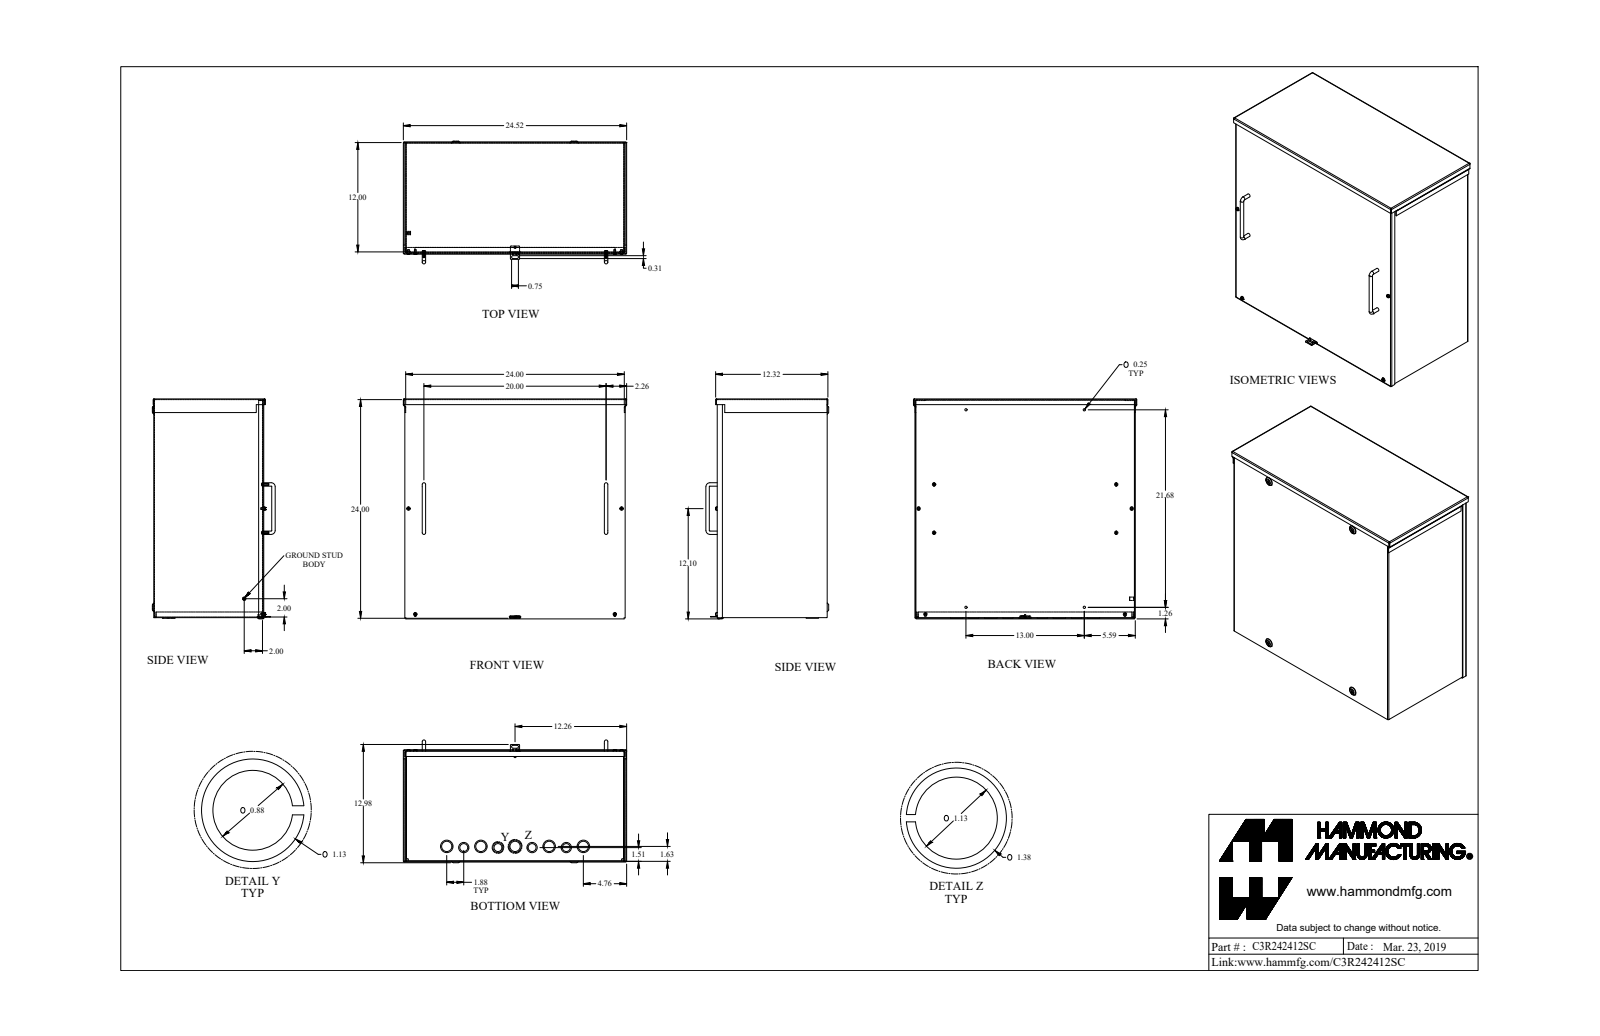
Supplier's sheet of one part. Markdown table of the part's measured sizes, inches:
| quantity | value |
| --- | --- |
| part name | C3R242412SC_Default |
| STEP written by | SolidWorks 2019 (CONFIG_CONTROL_DESIGN) |
| units | inches |
| bodies | 17 solids, 609 faces (314 planar, 177 cylindrical, 118 other) |
| overall size | 24.519 × 24.135 × 13.478 |
| volume | 179.7 in³ |
| surface area | 4 994 in² |
| round holes (diameter × count) | 0.156 × 5, 0.17 × 4, 0.203 × 4, 0.25 × 4, 0.875 × 4, 1.125 × 3, 1.125 × 2, 0.125 × 1, 0.137 × 1 |
| round bosses / shafts (diameter × count) | 0.375 × 9, 0.19 × 8, 1.375 × 5, 1.125 × 4, 0.367 × 4, 0.375 × 2, 0.125 × 1 |
| partial cylindrical surfaces (radius × count) | 0.036 × 20, 0.108 × 20, 0.109 × 8, 0.125 × 8, 0.156 × 2, 0.029 × 1, 0.086 × 1 |
| main face-to-face distances | 0.072, 12, 23.928, 11.928, 12.072, 24, 0.072, 23.856, 23.856, 23.928 |
| hole center spacings | 20, 3.75, 7.5, 0.024, 1.879, 1.88, 3.146, 5.3 |
